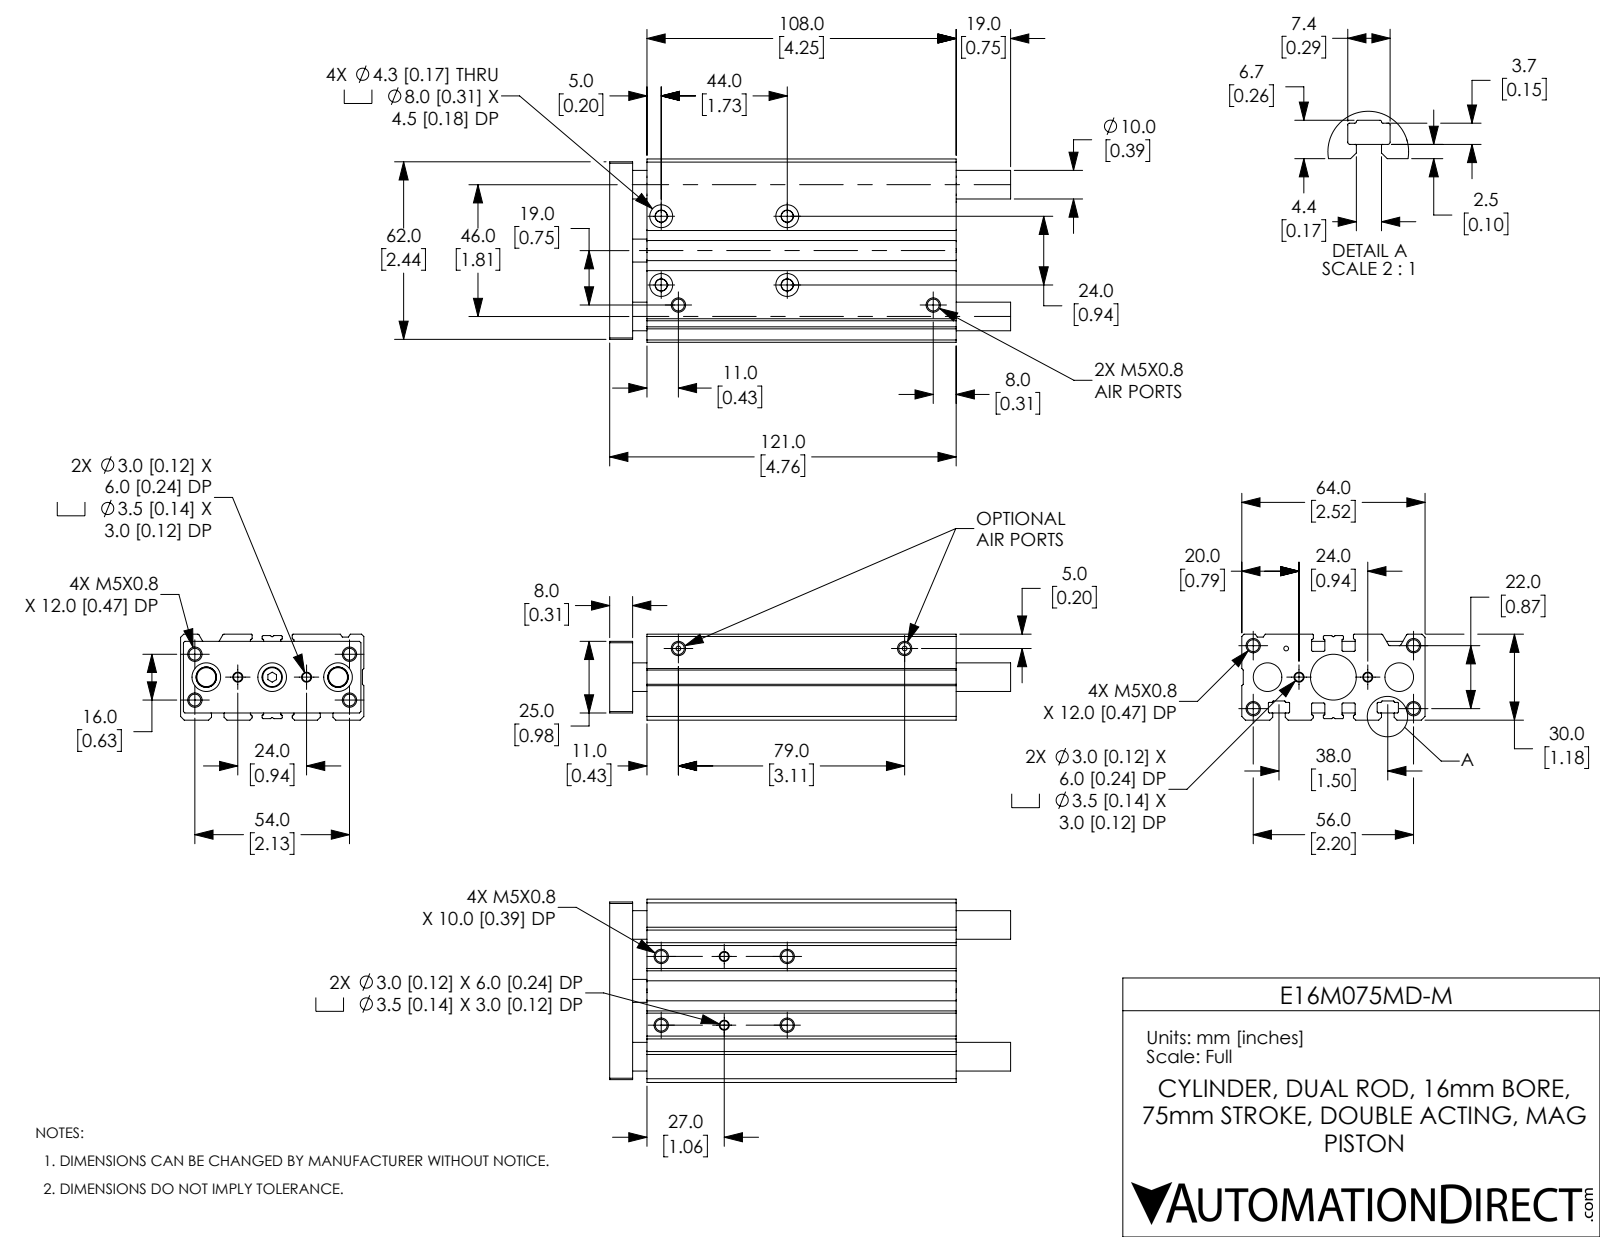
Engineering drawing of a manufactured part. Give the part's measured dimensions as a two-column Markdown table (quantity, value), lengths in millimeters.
| quantity | value |
| --- | --- |
| part name | E16M075MD-M_ENDPLATE; E16M075MD-M; E16M075MD-M_BODY |
| STEP written by | SolidWorks 2019 (CONFIG_CONTROL_DESIGN) |
| units | millimeters |
| bodies | 5 solids, 411 faces (133 planar, 192 cylindrical, 86 other) |
| overall size | 140 × 64 × 30 |
| volume | 183 051 mm³ |
| surface area | 66 501 mm² |
| round holes (diameter × count) | 4.13 × 16, 3 × 4, 3.5 × 4, 4.3 × 4, 8 × 4, 1.67 × 3, 5 × 3, 10 × 3, 7.11 × 2, 10 × 1, 16 × 1, 16 × 1 |
| round bosses / shafts (diameter × count) | 8 × 1, 7.11 × 1 |
| partial cylindrical surfaces (radius × count) | 0.2 × 22, 0.4 × 20, 0.25 × 8, 0.3 × 6, 0.5 × 4 |
| main face-to-face distances | 30, 0.5, 6, 64, 29, 3.5, 24, 24.4, 27.5, 35 |
| hole center spacings | 22, 3.16, 8.94, 12.08, 17, 19.03, 19.42, 24 |
